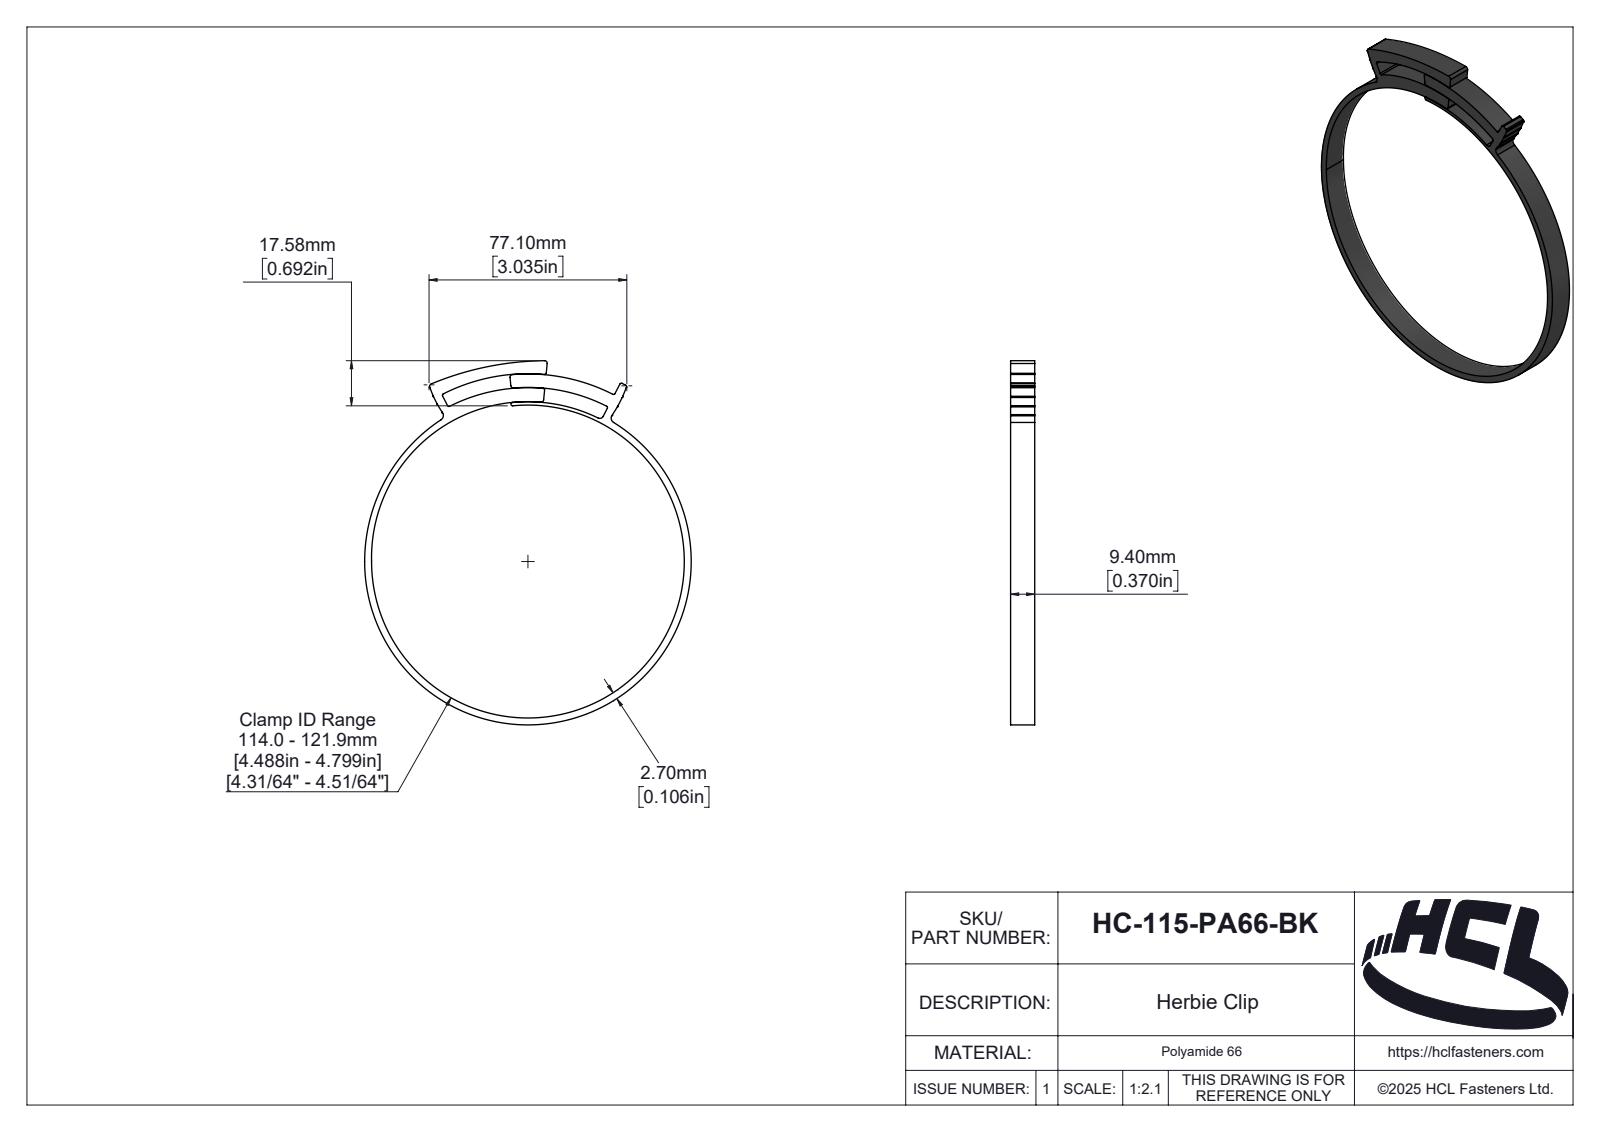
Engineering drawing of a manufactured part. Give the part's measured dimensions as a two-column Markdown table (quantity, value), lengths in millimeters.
| quantity | value |
| --- | --- |
| part name | HC-115-PA66-BK |
| STEP written by | SolidWorks 2025 (AUTOMOTIVE_DESIGN) |
| units | millimeters |
| bodies | 1 solid, 162 faces (13 planar, 100 cylindrical, 49 other) |
| overall size | 141.9 × 127.3 × 9.4 |
| volume | 15 392 mm³ |
| surface area | 13 033 mm² |
| partial cylindrical surfaces (radius × count) | 0.25 × 8, 0.6 × 6, 1 × 5, 2 × 2, 0.17 × 1, 0.65 × 1, 0.67 × 1, 0.84 × 1 |
| main face-to-face distances | 9.4 |
